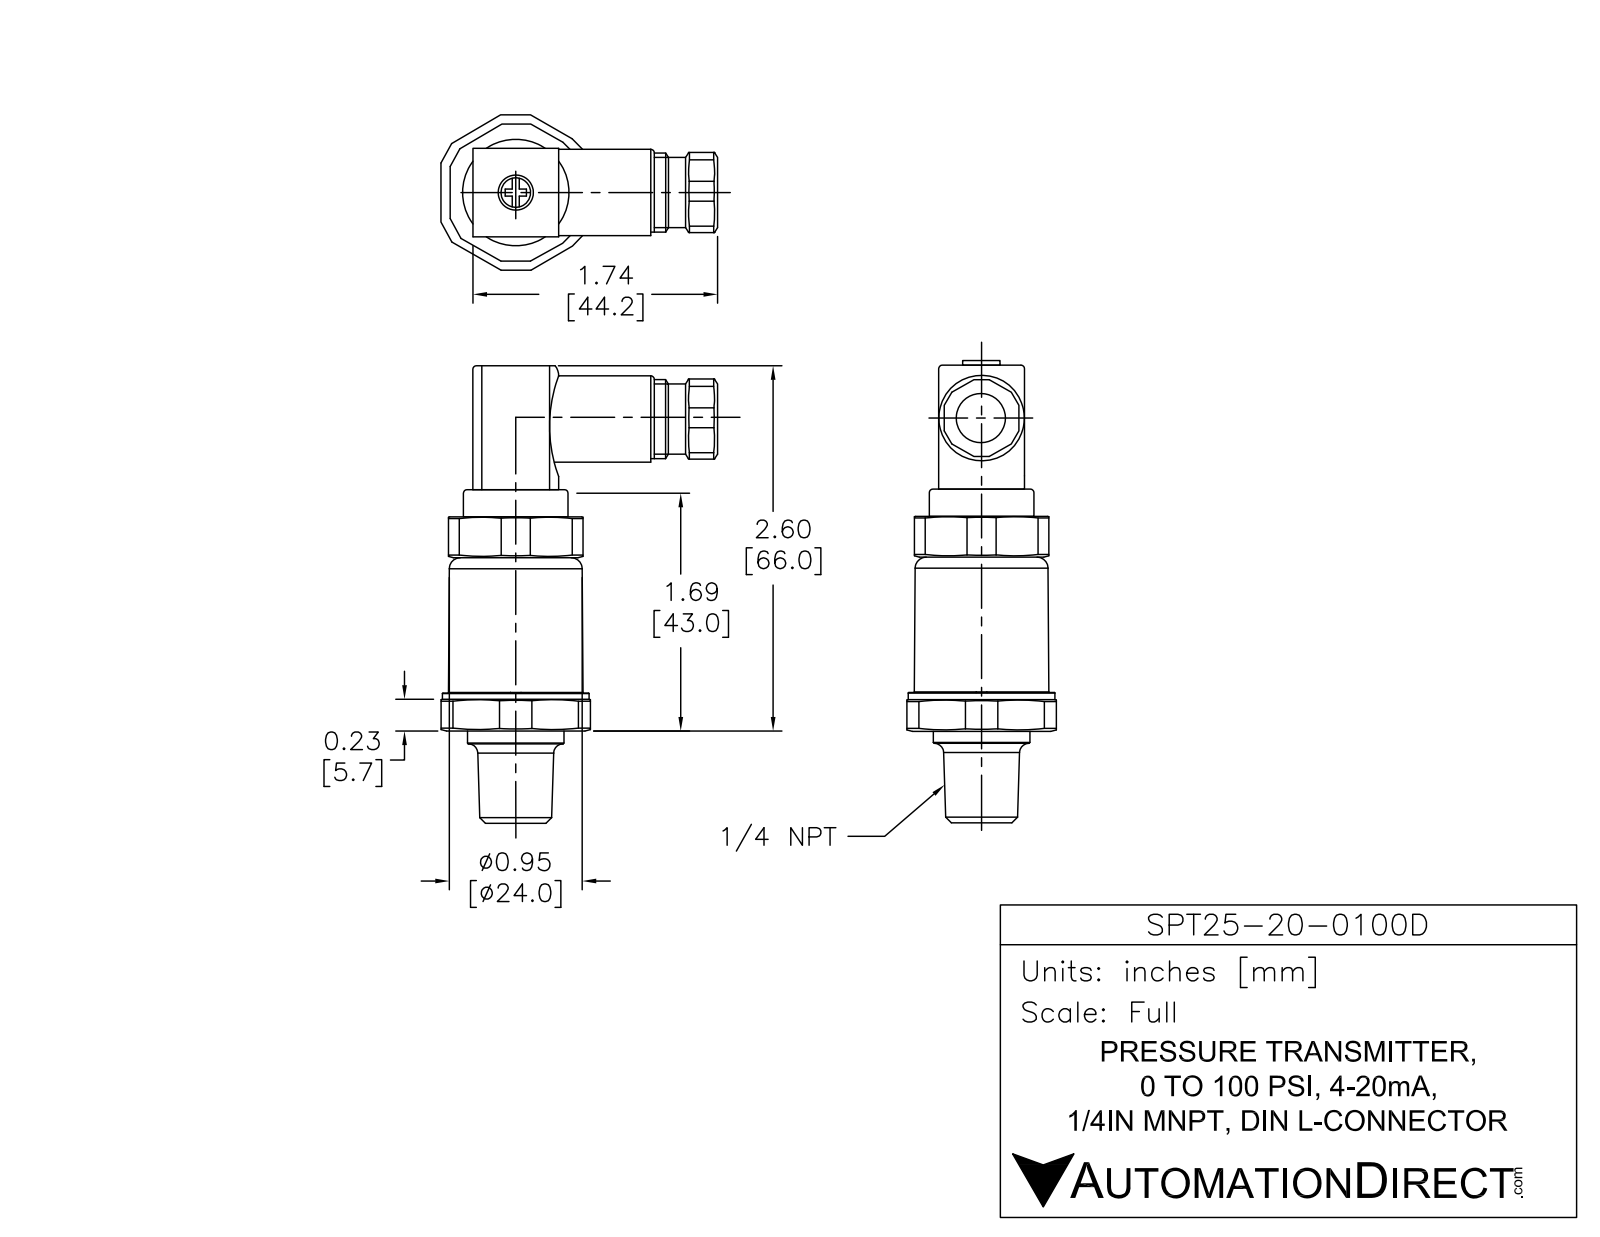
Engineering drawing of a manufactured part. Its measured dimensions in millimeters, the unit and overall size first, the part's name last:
Units: millimetres
Overall size (bounding box): 81.25 × 38.01 × 35.71
Round holes (diameter × count): ⌀1 ×1, ⌀3.3 ×1, ⌀7 ×1, ⌀8 ×1
Round bosses / shafts (diameter × count): ⌀26.75 ×1, ⌀24 ×1, ⌀17.5 ×1, ⌀15 ×1, ⌀14 ×1, ⌀11 ×1
Partial cylindrical surfaces — rounded edges, fillets, slot ends (radius × count): R1.5 ×8, R1.15 ×4, R2.25 ×4, R2 ×3, R1.15 ×1, R1.17 ×1, R14.5 ×1
Main face-to-face distances: 1.5, 29.5, 31, 15.75, 0.35, 15.4, 6.75, 37.75, 36.25, 5
Hole centre spacings: 1.33
Volume: 27 900 mm³ · Surface area: 10 134 mm²
Bodies: 5 solids, 170 faces (96 planar, 64 cylindrical, 10 other)
Part name (STEP PRODUCT): SPT25-20-0100D
STEP written by: SolidWorks 2011 (AUTOMOTIVE_DESIGN)
